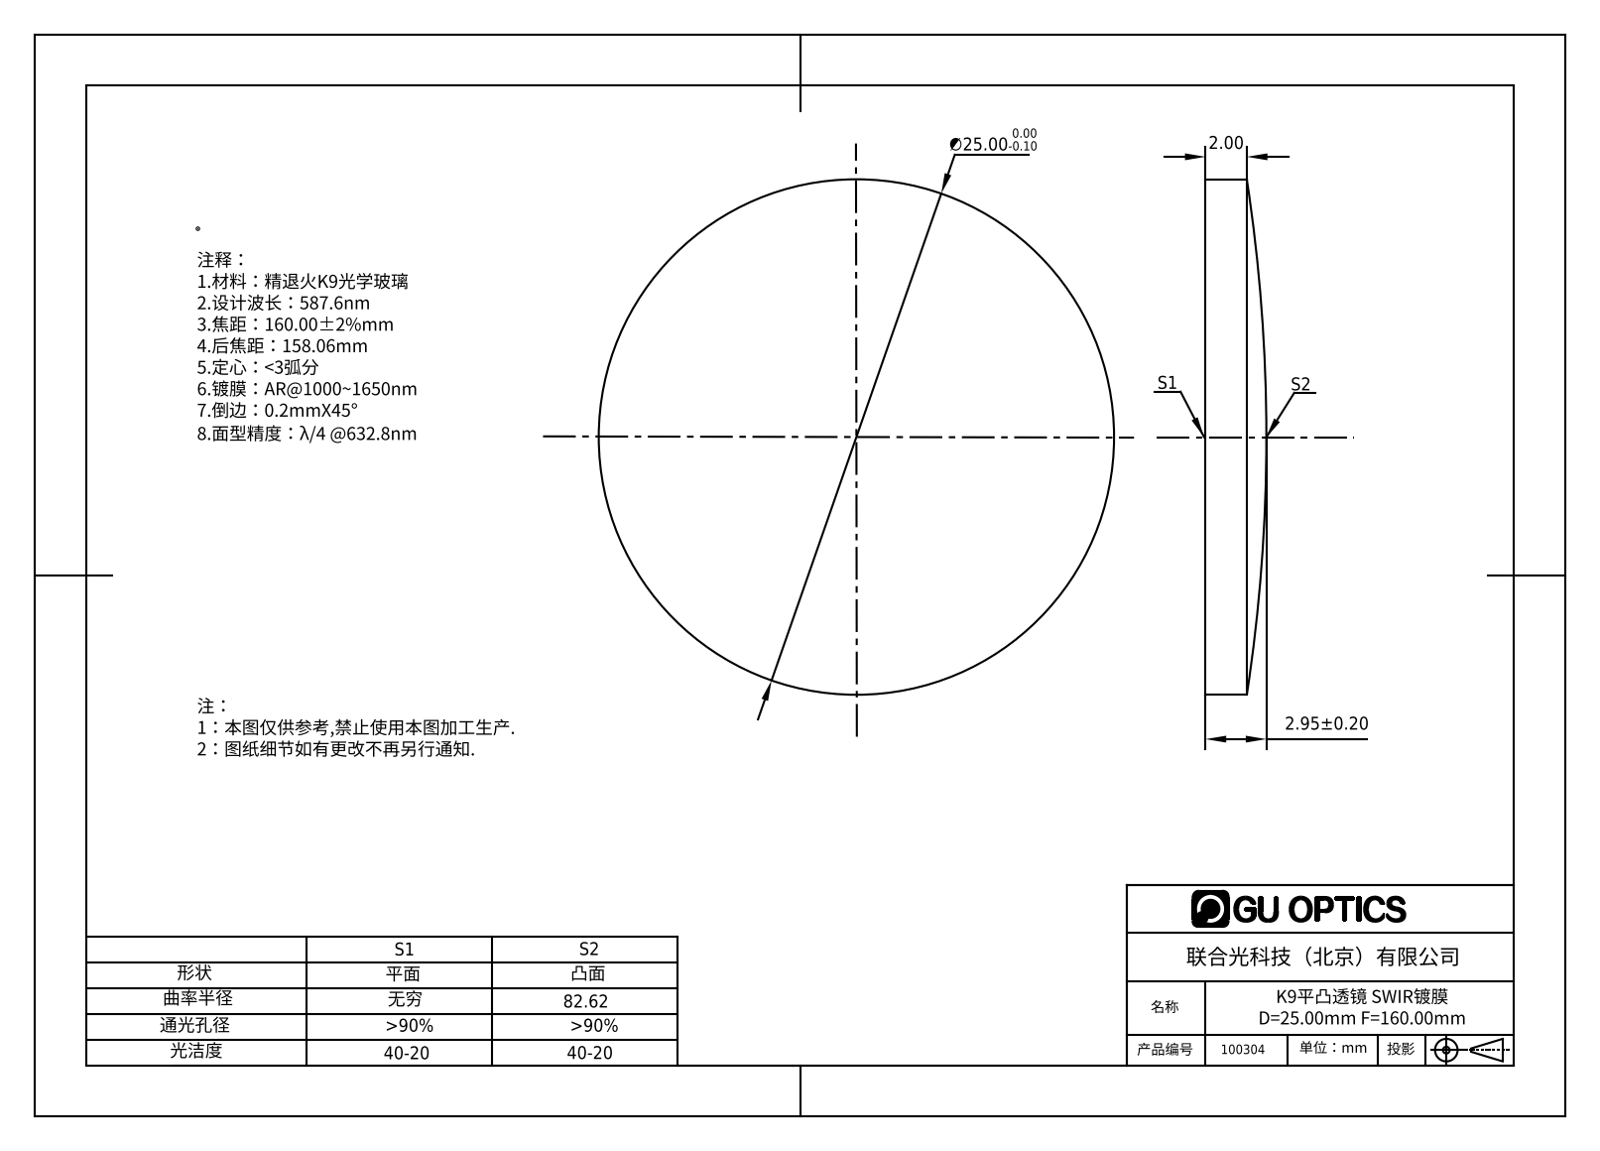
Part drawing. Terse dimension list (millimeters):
name: 100132
written by: SolidWorks 2016 (AUTOMOTIVE_DESIGN)
unit: mm
bodies: 1 solid, 5 faces (1 planar, 2 cylindrical, 2 other)
size: 25 × 25 × 2.95
volume: 1 215 mm³; area: 1 142 mm²
bosses: 1× ⌀25
